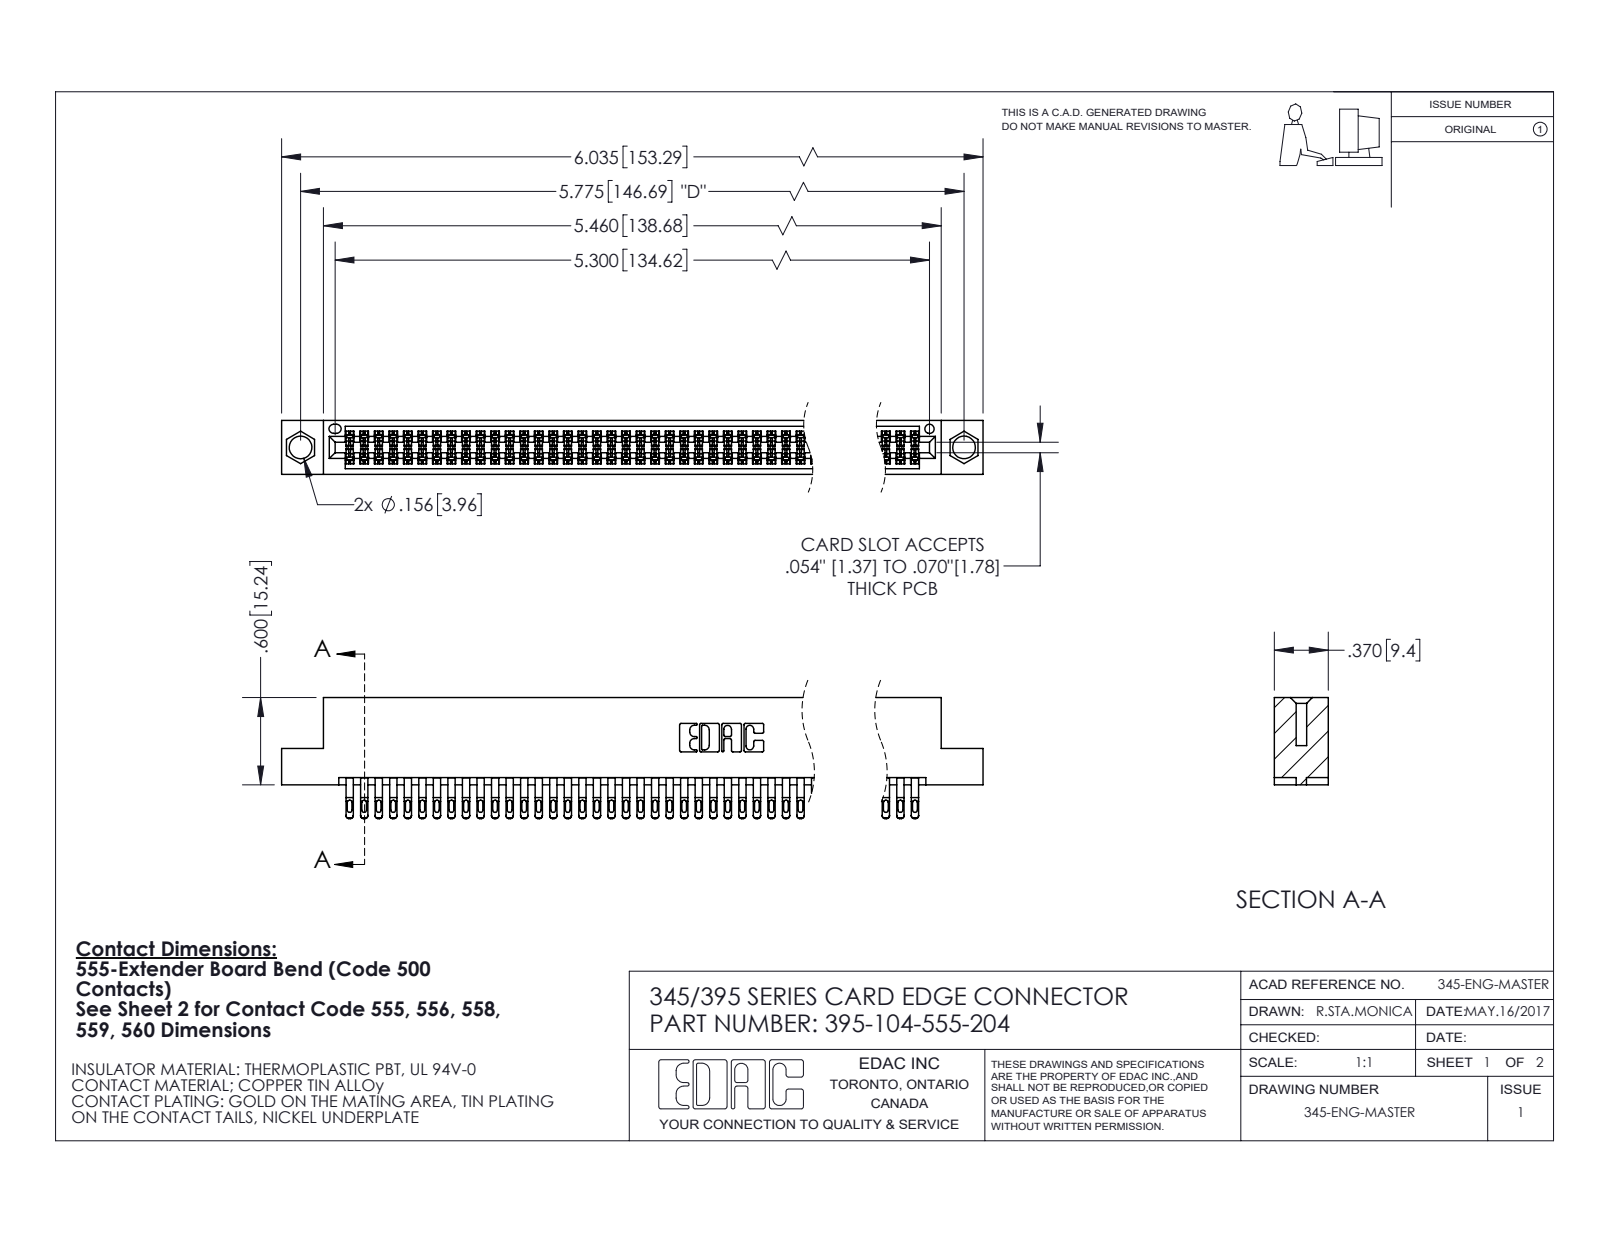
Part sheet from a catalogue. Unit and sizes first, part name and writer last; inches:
Units: inches
Overall size (bounding box): 6.035 × 0.832 × 0.37
Round holes (diameter × count): ⌀0.156 ×2, ⌀0.064 ×1
Partial cylindrical surfaces — rounded edges, fillets, slot ends (radius × count): R0.016 ×260, R0.006 ×208, R0.02 ×208, R0.01 ×22, R0.007 ×6, R0.031 ×6, R0.026 ×3, R0.01 ×2
Main face-to-face distances: 0.298, 0.072, 0.025, 0.37, 0.2, 0.098, 0.272, 0.225, 0.175, 0.149
Hole centre spacings: 0.27, 5.539, 5.775
Volume: 0.926 in³ · Surface area: 36.47 in²
Bodies: 105 solids, 5964 faces (3318 planar, 2646 cylindrical, 0 other)
Part name (STEP PRODUCT): 345 Part_Flush Mounting Lugs - 0.156 Dia-TI; 395-104-555-204; 345-292-001_555 Tail
STEP written by: SolidWorks 2020 (CONFIG_CONTROL_DESIGN)
